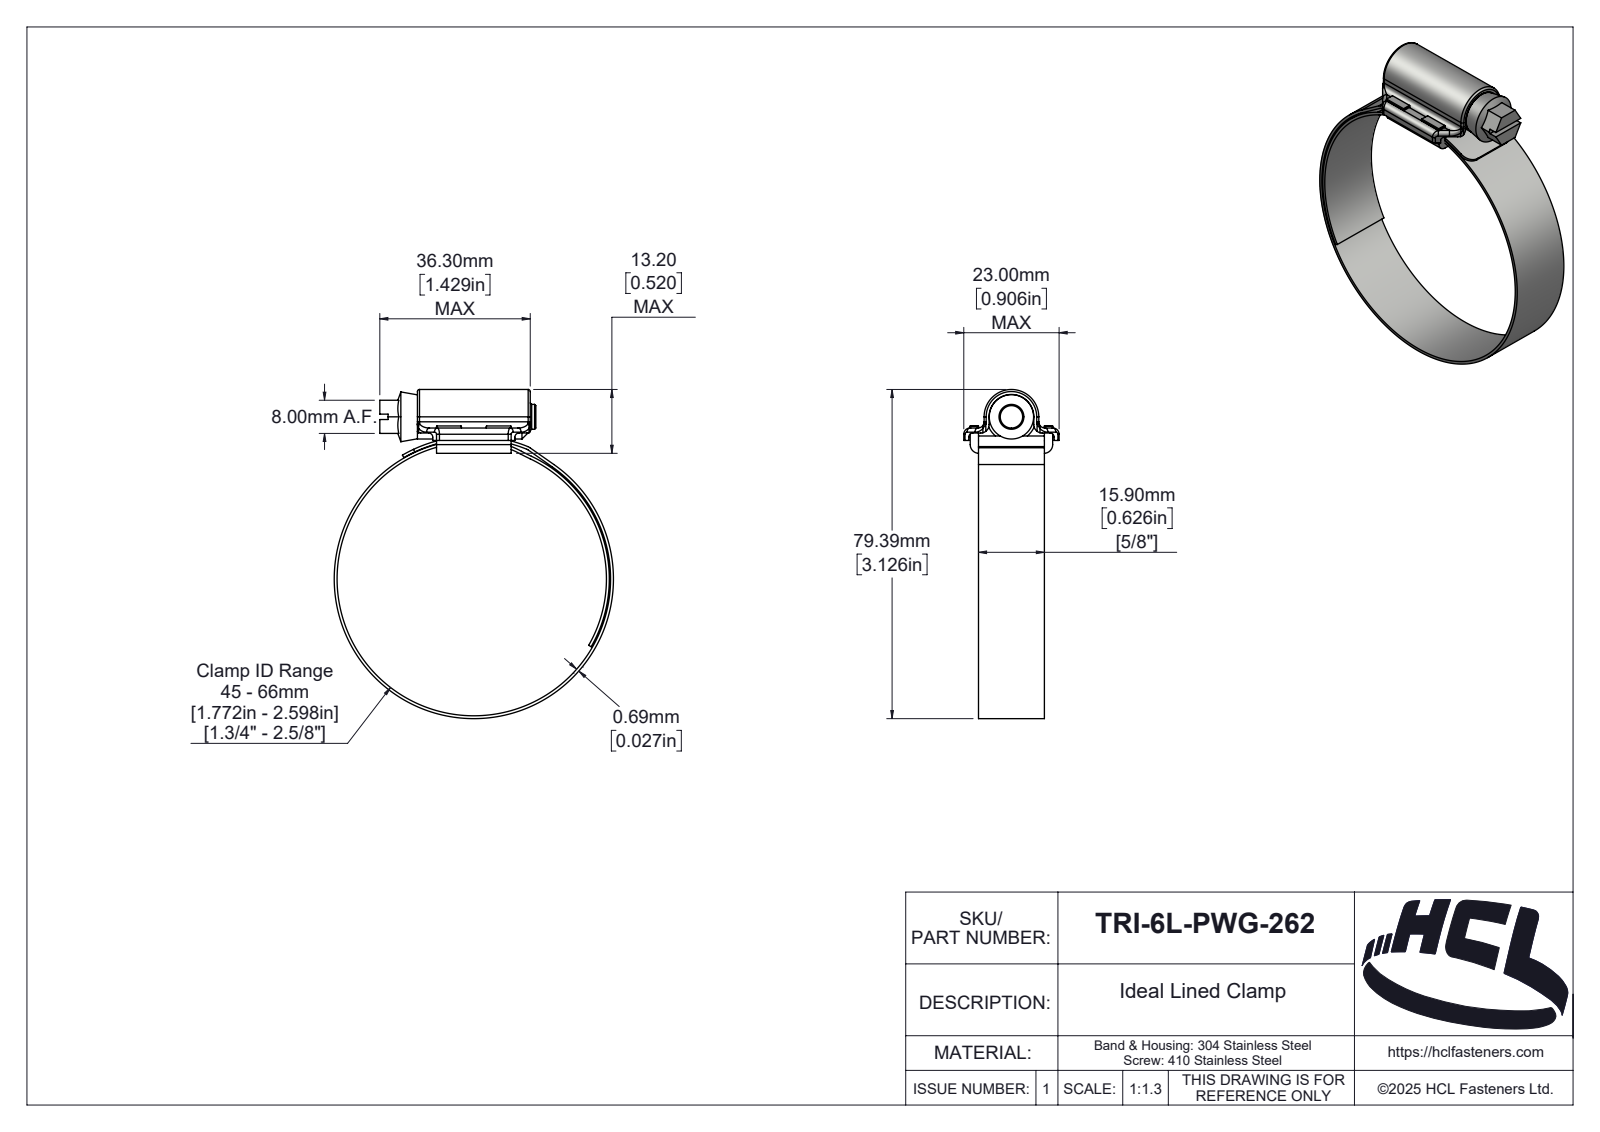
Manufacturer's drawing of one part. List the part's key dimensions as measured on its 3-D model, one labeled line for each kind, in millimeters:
Part name (STEP PRODUCT): TRI-6L-PWG-262
STEP written by: SolidWorks 2025 (AUTOMOTIVE_DESIGN)
Units: millimetres
Bodies: 4 solids, 268 faces (87 planar, 102 cylindrical, 79 other)
Overall size (bounding box): 79.39 × 67.38 × 23
Volume: 8 438 mm³ · Surface area: 14 417 mm²
Round holes (diameter × count): ⌀66 ×1
Round bosses / shafts (diameter × count): ⌀67.38 ×1, ⌀10.7 ×1, ⌀6 ×1
Partial cylindrical surfaces — rounded edges, fillets, slot ends (radius × count): R1 ×14, R0.5 ×4, R1.5 ×4, R2 ×3, R0.1 ×2, R2.1 ×2, R3 ×2, R0.46 ×1
Main face-to-face distances: 2, 15.9, 17.9, 4.9, 1.2, 4.55, 3.35, 0.69, 15.35, 2.55
